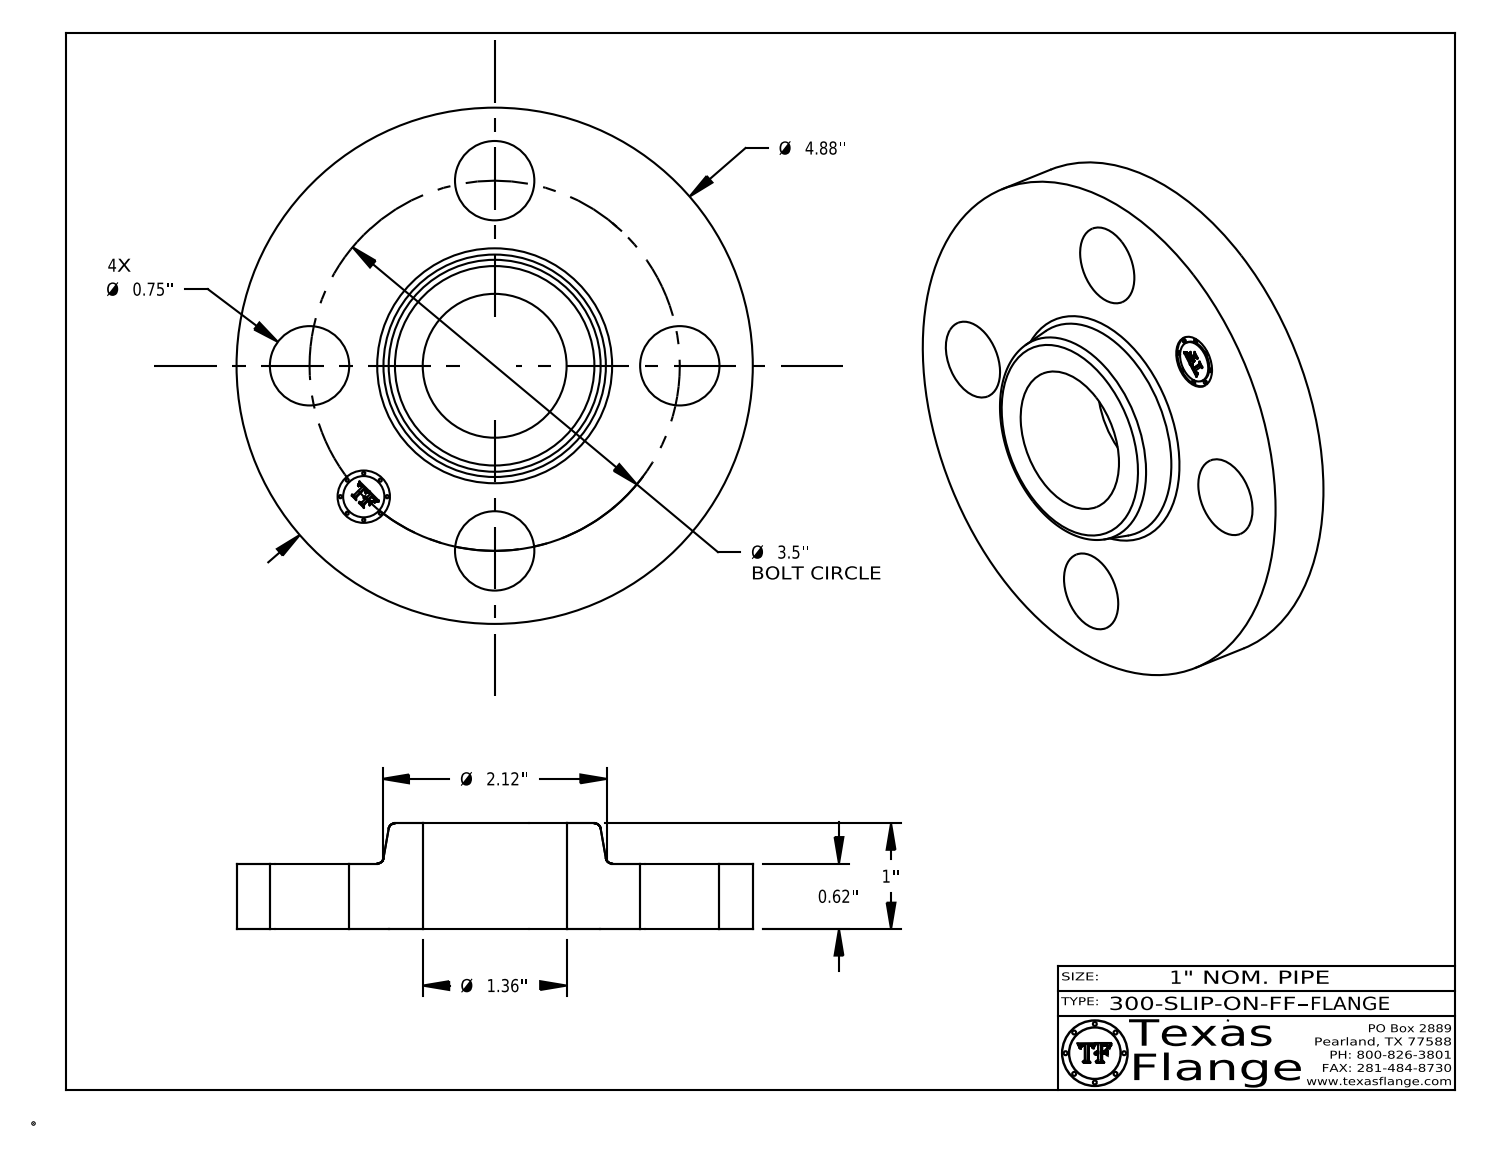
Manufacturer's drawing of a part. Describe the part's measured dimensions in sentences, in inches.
The part is named "300-SLIP-ON-FF". Its 3-D file was written by "CATIA V5 STEP AP214 (AUTOMOTIVE_DESIGN)". It is 1 solid with 407 faces: 369 planar, 32 cylindrical and 6 other. Overall it measures 4.88 by 4.88 by 1 inches. Its volume is 10.31 cubic inches and its surface area 52.52 square inches. Round holes: 4 of diameter 0.75, 1 of diameter 0.495, 1 of diameter 1.36. Round bosses or shafts: 8 of diameter 0.03, 1 of diameter 4.88, 1 of diameter 0.39. The main face-to-face distances are 0.62, 1, 0.38, 0.015, 0.605, 0.395, 0.148, 0.145, 0.027, 0.096. The hole center spacings are 1.75, 2.475, 1.339, 3.233, 3.5.
